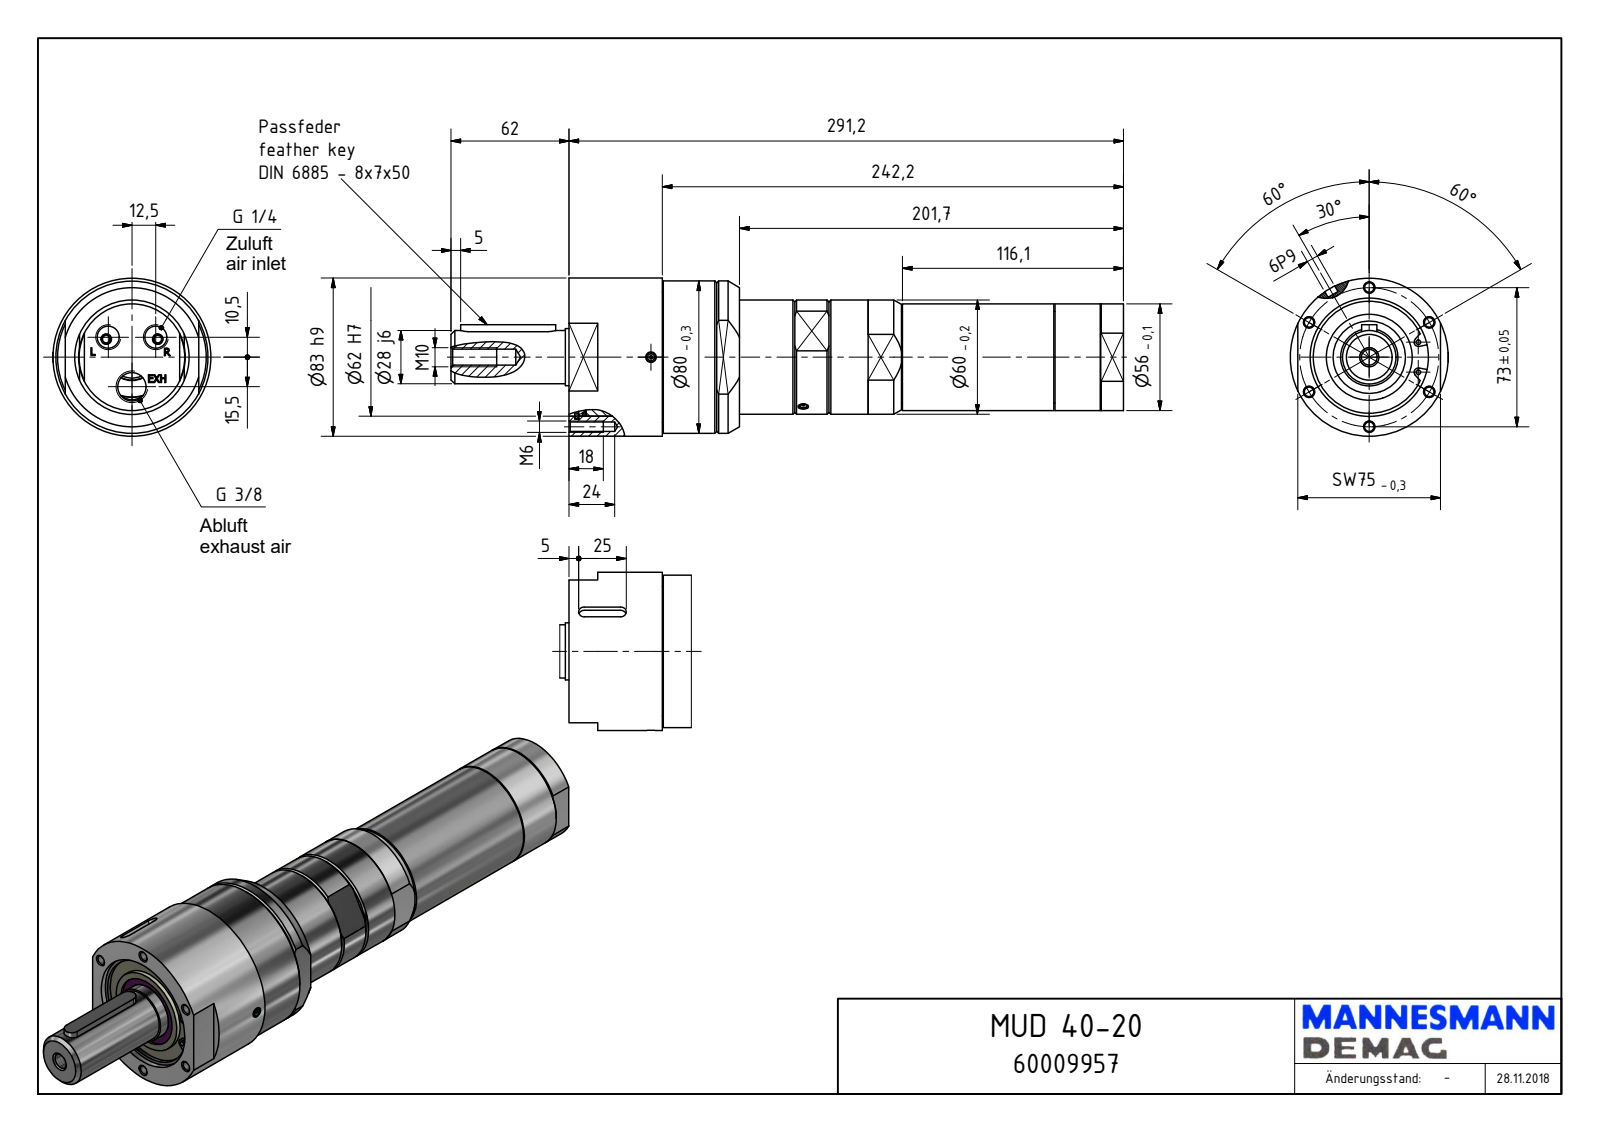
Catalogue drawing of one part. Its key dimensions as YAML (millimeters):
part_name: "MUD 40-20_60009957"
step_written_by: "Autodesk Inventor 2018 (AUTOMOTIVE_DESIGN)"
units: millimeters
bodies: {solids: 1, faces: 601, planar: 240, cylindrical: 287, other: 74}
overall_size: [353.2, 83, 83]
volume: 1000000
surface_area: 99036
round_holes:
  - {diameter: 4.92, count: 6}
  - {diameter: 1.55, count: 2}
  - {diameter: 2.5, count: 2}
  - {diameter: 4, count: 2}
  - {diameter: 5.5, count: 2}
  - {diameter: 11.45, count: 2}
  - {diameter: 8.38, count: 1}
  - {diameter: 14.95, count: 1}
  - {diameter: 36.5, count: 1}
  - {diameter: 38, count: 1}
  - {diameter: 40, count: 1}
  - {diameter: 48.38, count: 1}
round_bosses_or_shafts:
  - {diameter: 5, count: 2}
  - {diameter: 3.6, count: 2}
  - {diameter: 83, count: 1}
  - {diameter: 80, count: 1}
  - {diameter: 68.18, count: 1}
  - {diameter: 67, count: 1}
  - {diameter: 60, count: 1}
  - {diameter: 56, count: 1}
partial_cylinders:
  - {radius: 3.5, count: 94}
  - {radius: 2.25, count: 2}
  - {radius: 3, count: 2}
  - {radius: 4, count: 2}
  - {radius: 6, count: 2}
  - {radius: 6.47, count: 2}
  - {radius: 7.69, count: 1}
  - {radius: 19.64, count: 1}
face_to_face_distances: [2.5, 291.2, 49, 242.2, 0.5, 10, 62.5, 89.5, 40.5, 201.7]
hole_center_spacings: [36.5, 63.22, 28.85, 73, 11.89, 16.32, 20.62, 26.77]
